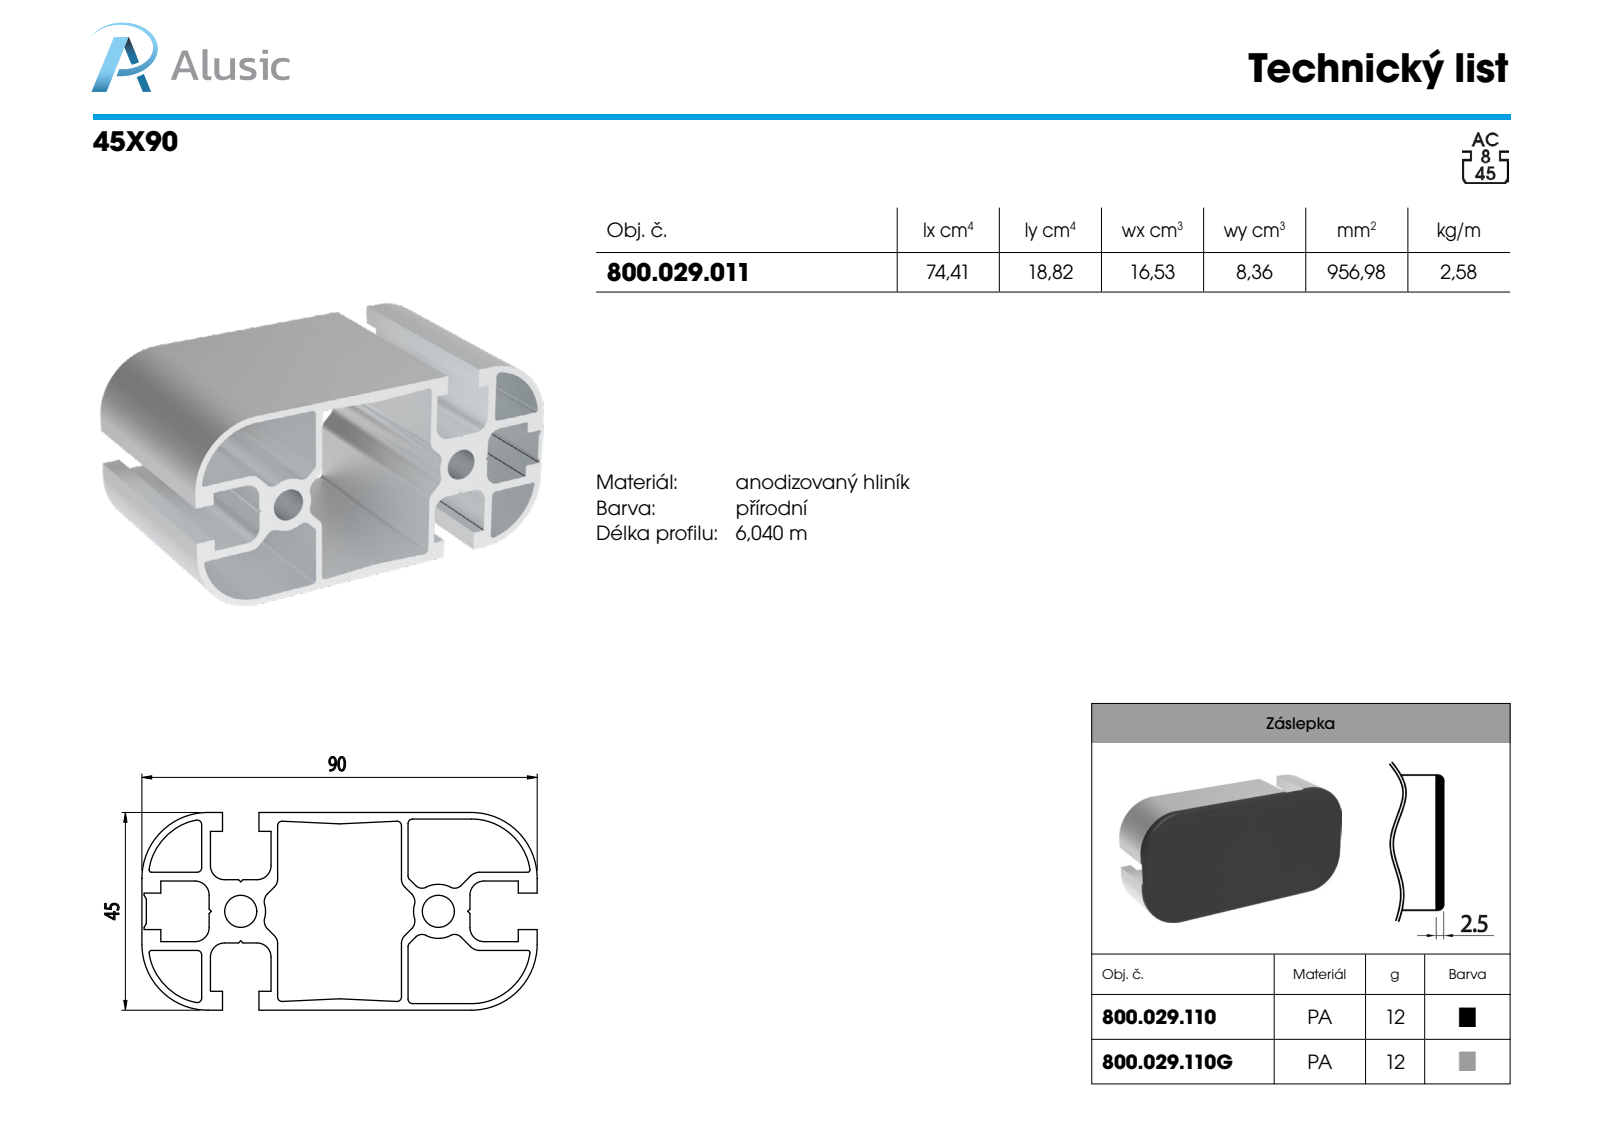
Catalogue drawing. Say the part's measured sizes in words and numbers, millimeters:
The part is named "800.029.011". Its 3-D file was written by "SolidWorks 2018 (AUTOMOTIVE_DESIGN)". It is 1 solid with 140 faces: 80 planar, 60 cylindrical and 0 other. Overall it measures 100 by 90 by 45 millimeters. Its volume is 95 698 cubic millimeters and its surface area 85 983 square millimeters. Round holes: 2 of diameter 7.3. Partial cylindrical surfaces (rounded edges, fillets, slot ends): 12 of radius 1, 8 of radius 2.5, 8 of radius 3.2, 4 of radius 0.5, 4 of radius 2, 4 of radius 13.5, 4 of radius 15, 2 of radius 3. The main face-to-face distances are 45, 1.5, 15.6, 13.6, 29.4, 14.1, 29.7, 2, 15.8, 13.8. The hole center spacings are 45.
